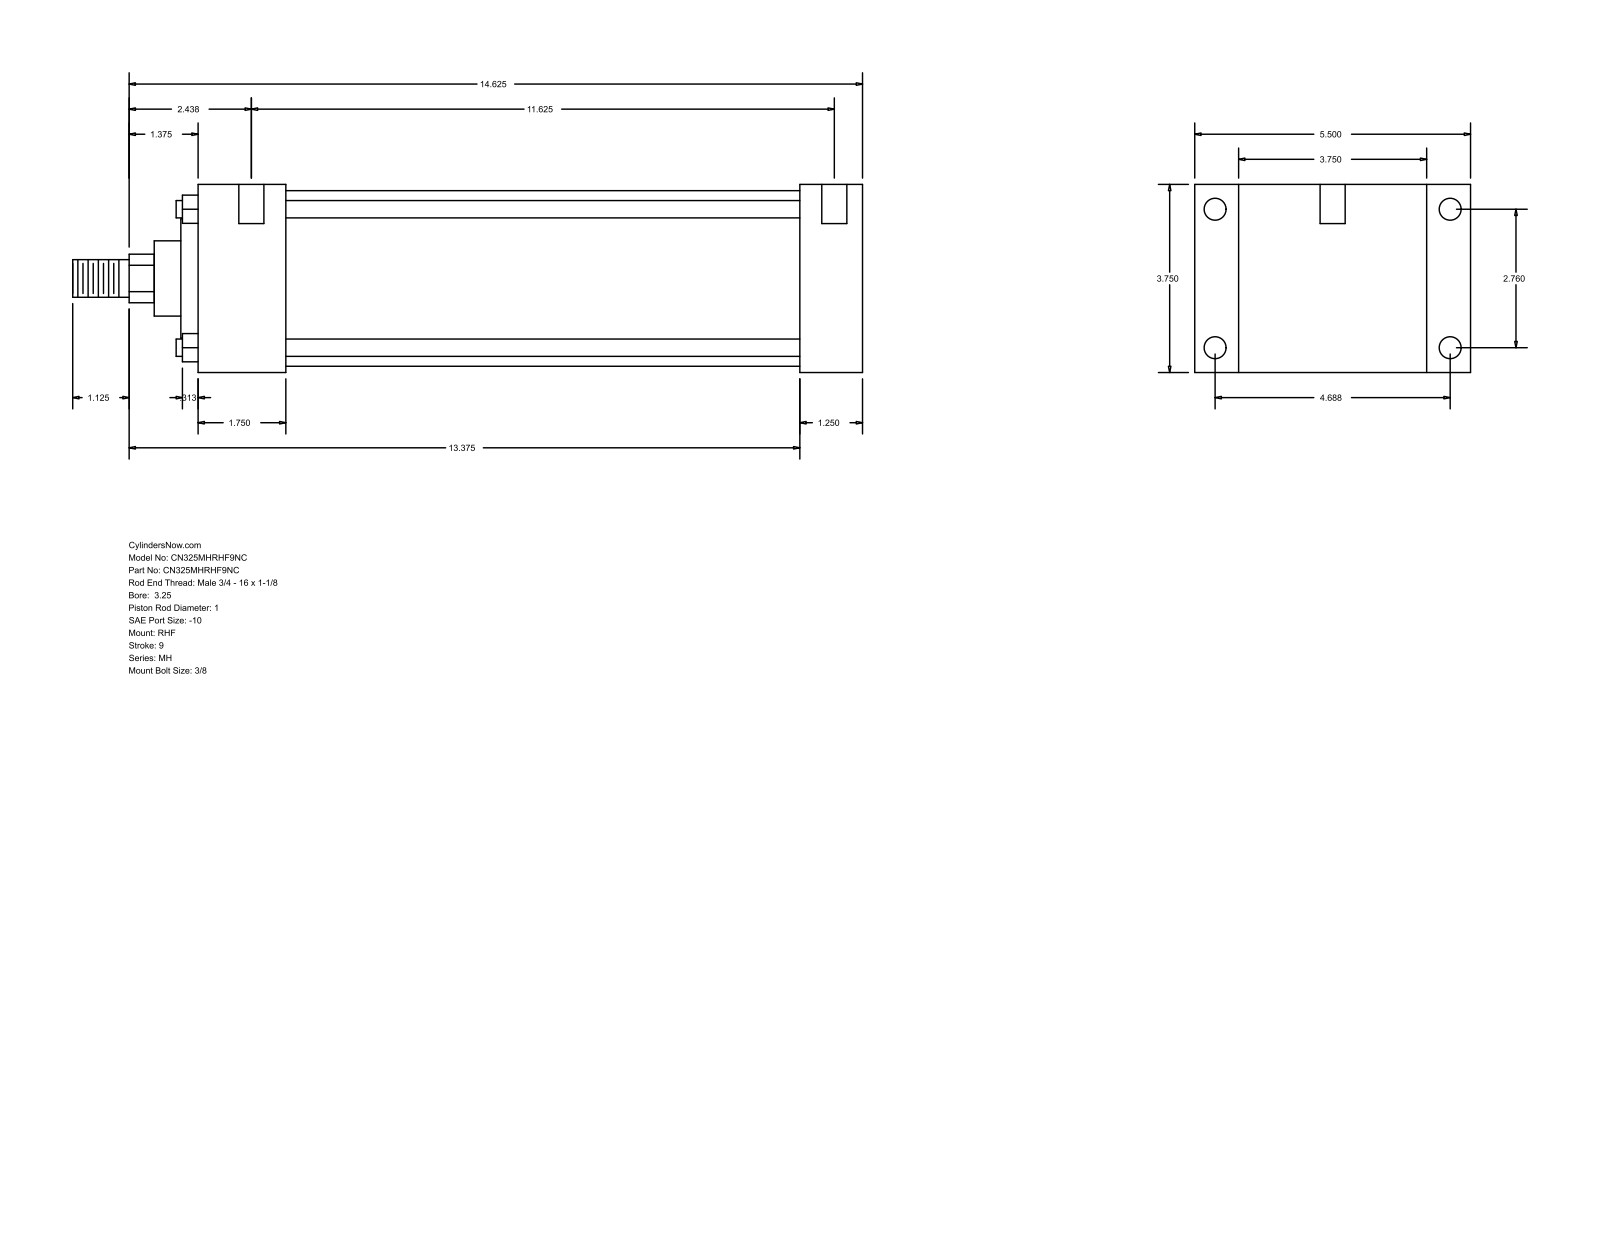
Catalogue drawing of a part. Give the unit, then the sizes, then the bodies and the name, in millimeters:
Units: millimetres
Overall size (bounding box): 400.05 × 139.7 × 95.25
Round holes (diameter × count): ⌀5.56 ×4, ⌀11.13 ×4, ⌀12.7 ×2
Round bosses / shafts (diameter × count): ⌀8.76 ×4, ⌀88.9 ×1, ⌀60.33 ×1, ⌀38.1 ×1, ⌀25.4 ×1, ⌀19.05 ×1
Partial cylindrical surfaces — rounded edges, fillets, slot ends (radius × count): R12.29 ×1
Main face-to-face distances: 95.24, 31.75, 22.23, 117.47, 304.81, 336.56, 139.7, 44.46, 260.35, 292.1
Hole centre spacings: 70.1, 119.06, 138.16, 301.62, 1.58, 4.76, 295.28, 296.86
Bodies: 0 solids, 90 faces (61 planar, 29 cylindrical, 0 other)
Part name (STEP PRODUCT): MH_RHF__0325_1
STEP written by: GSSL Pune (CONFIG_CONTROL_DESIGN)
